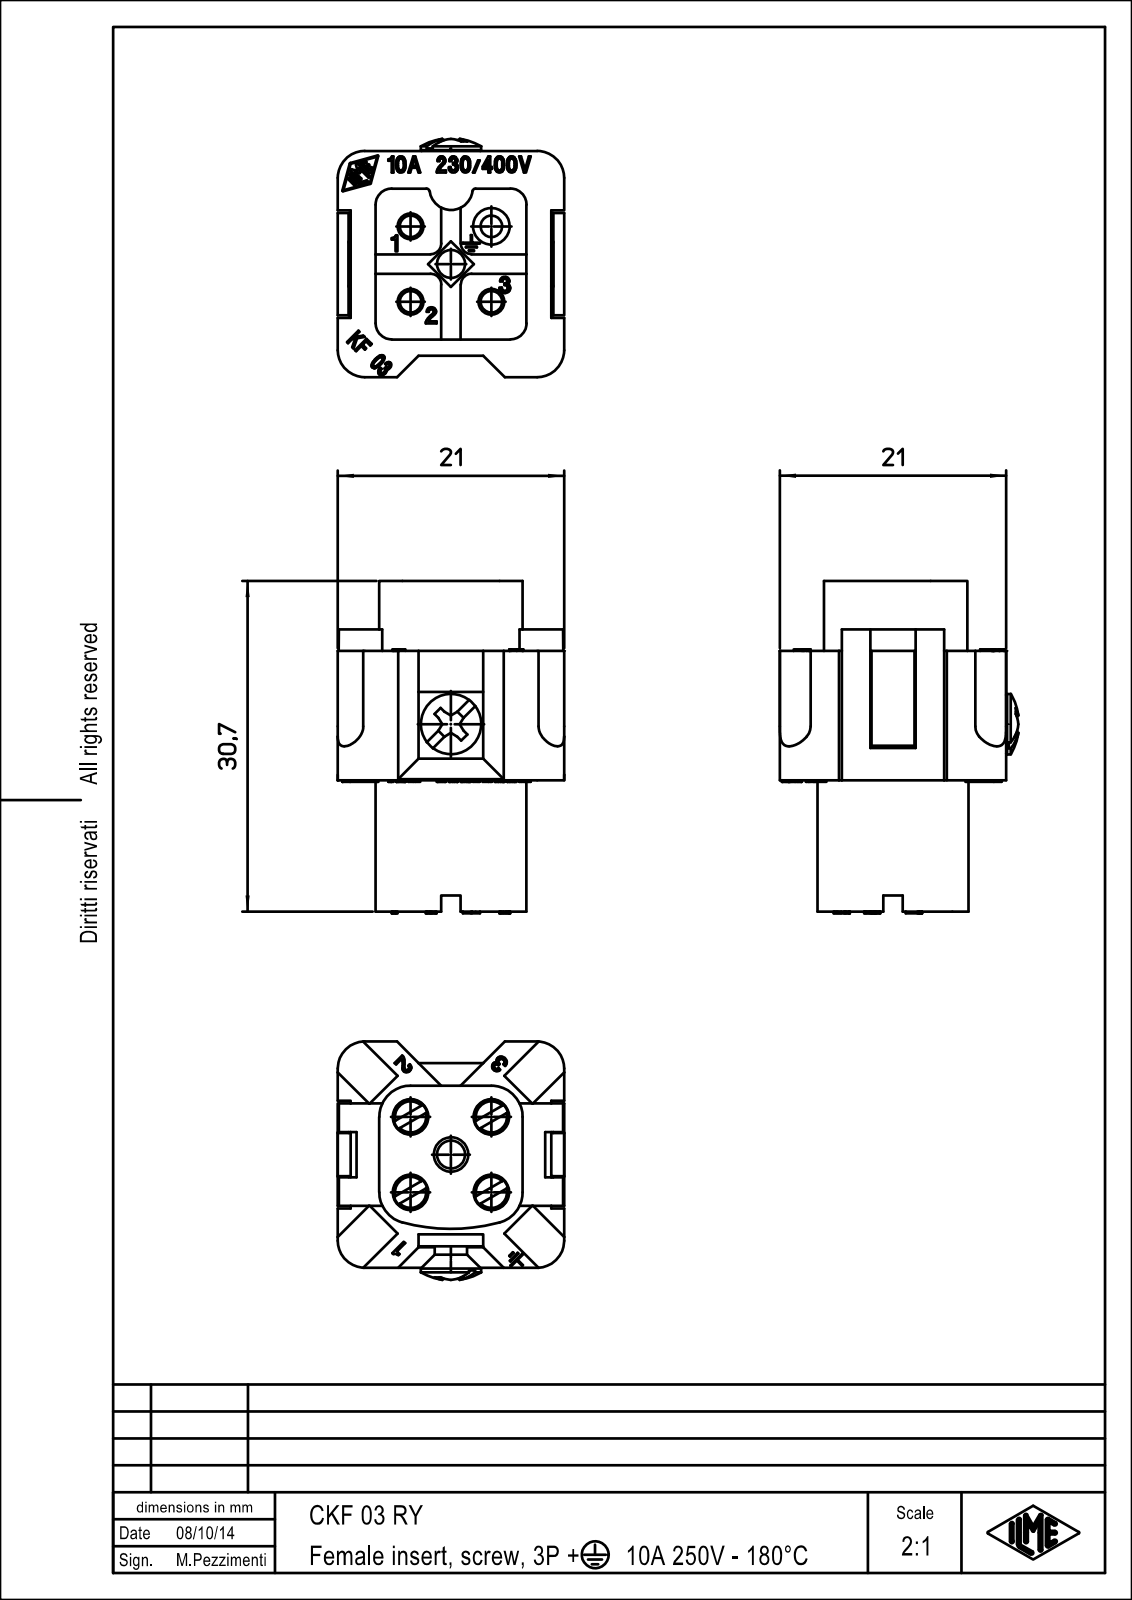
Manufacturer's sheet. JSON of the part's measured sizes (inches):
{"part_name": "CKF_03_RY", "step_written_by": "PTC Creo Elements/Direct Modeling 19.0B 21-Mar-2015 (C) Parametric Technology GmbH (AUTOMOTIVE_DESIGN)", "units": "inches", "bodies": {"solids": 1, "faces": 1040, "planar": 937, "cylindrical": 91, "other": 12}, "overall_size": [1.215, 0.871, 0.827], "volume_in3": 0.421, "surface_area_in2": 7.832, "round_holes": [[0.079, 8], [0.13, 4], [0.094, 3], [0.102, 1], [0.126, 1], [0.134, 1]], "round_bosses_or_shafts": [[0.126, 4], [0.22, 1], [0.118, 1]], "partial_cylinders_radius": [[0.039, 4], [0.059, 4], [0.073, 4], [0.098, 4], [0.114, 4], [0.012, 2], [0.007, 1], [0.079, 1]], "face_to_face_distances": [0.138, 0.689, 0.551, 0.118, 0.014, 0.642, 0.079, 0.091, 0.047, 0.421], "hole_center_spacings": [0.202, 0.014, 0.276, 0.295, 0.404]}
